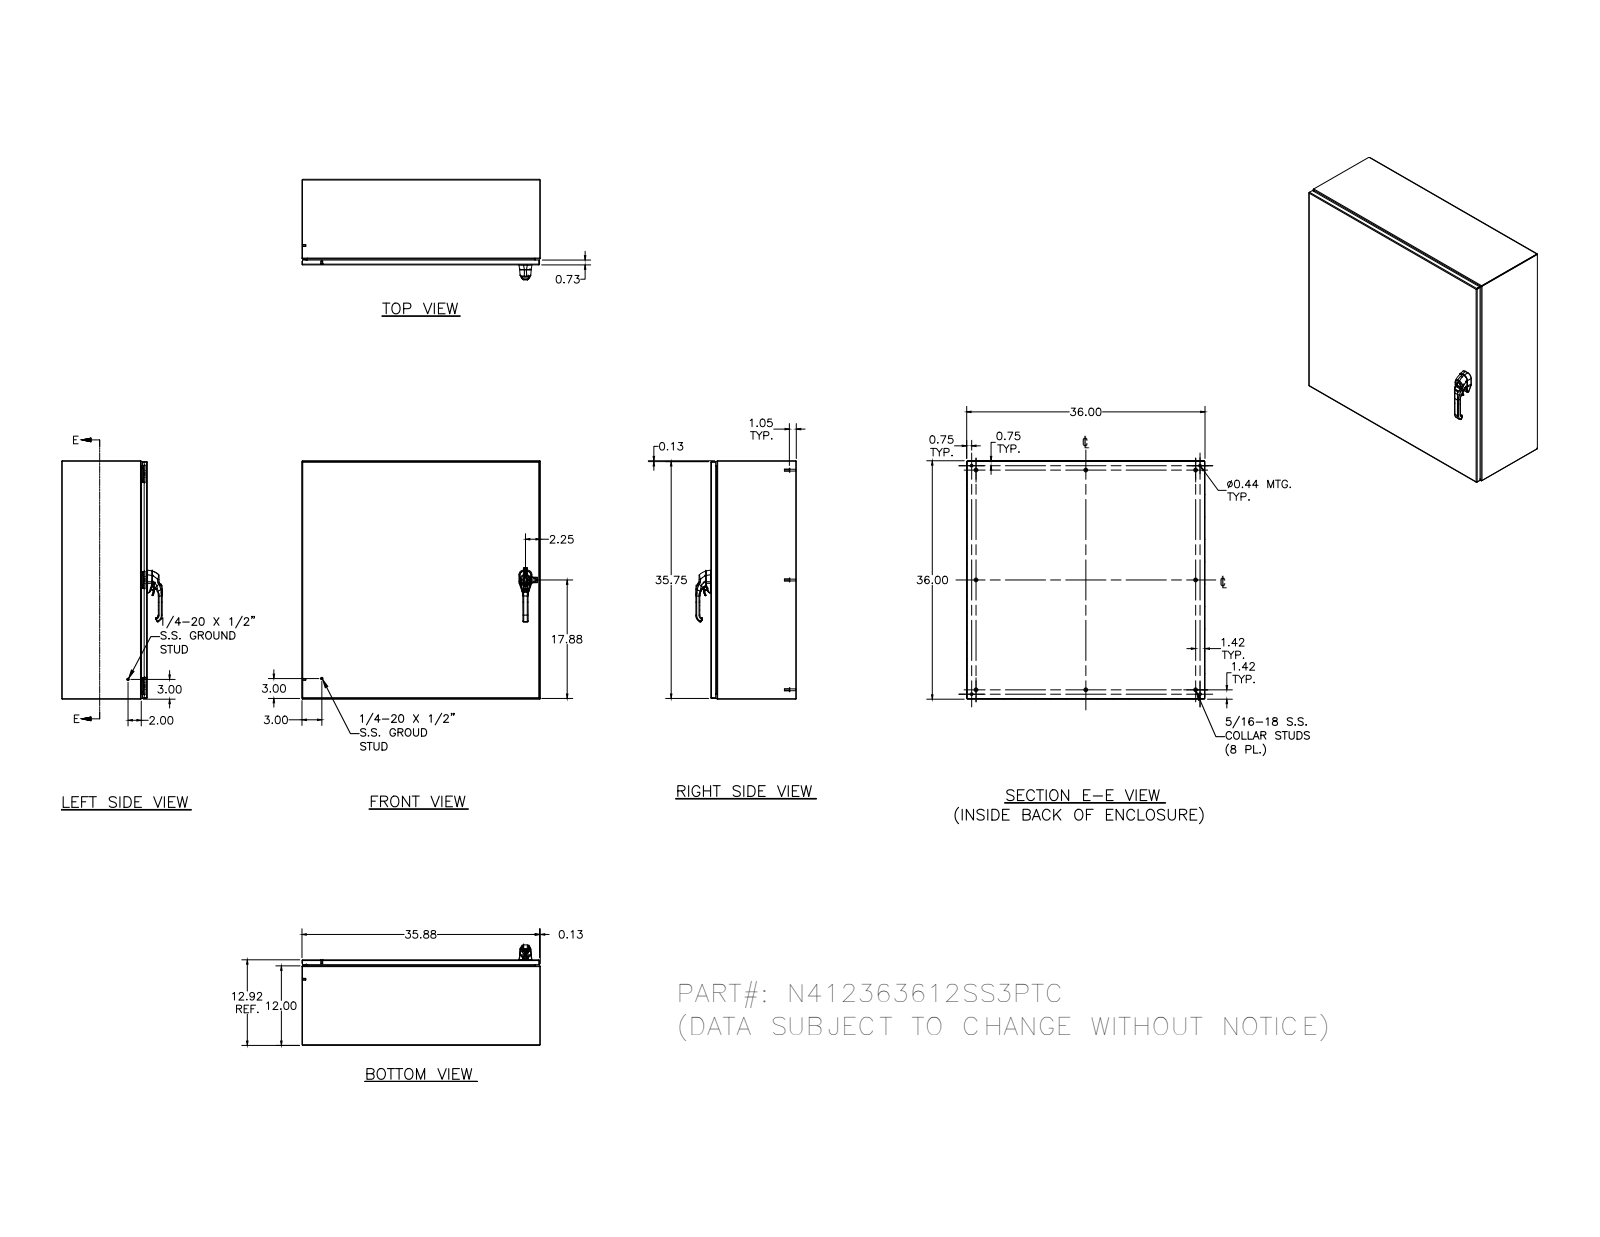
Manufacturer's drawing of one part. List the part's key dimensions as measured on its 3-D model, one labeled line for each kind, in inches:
Part name (STEP PRODUCT): N412363612SS3PTC; N412363612SS3PTCBTB; N4123612SS3PTCLS; N4123612SS3PTCRS (+8 more)
STEP written by: Autodesk Inventor 2011 (AUTOMOTIVE_DESIGN)
Units: inches
Bodies: 72 solids, 3434 faces (1153 planar, 1263 cylindrical, 1018 other)
Overall size (bounding box): 36 × 36 × 15.166
Volume: 351 in³ · Surface area: 9 388 in²
Round holes (diameter × count): ⌀0.093 ×6, ⌀0.152 ×6, ⌀0.167 ×6, ⌀0.172 ×6, ⌀0.187 ×6, ⌀0.165 ×5, ⌀0.437 ×4, ⌀0.156 ×3, ⌀0.213 ×3, ⌀0.106 ×2, ⌀0.16 ×2, ⌀0.169 ×2
Round bosses / shafts (diameter × count): ⌀0.25 ×14, ⌀0.563 ×8, ⌀0.3 ×8, ⌀0.275 ×8, ⌀0.36 ×6, ⌀0.32 ×6, ⌀0.256 ×6, ⌀0.164 ×6
Partial cylindrical surfaces — rounded edges, fillets, slot ends (radius × count): R0.02 ×188, R0.012 ×100, R0.05 ×38, R0.031 ×32, R0.016 ×26, R0.125 ×24, R0.019 ×23, R0.105 ×18
Main face-to-face distances: 0.074, 12.843, 35.926, 12.917, 12.769, 35.852, 36, 11.926, 0.917, 0.739
Hole centre spacings: 16, 32, 16.008, 34.5, 0.5, 0.656, 0.66, 1.307
